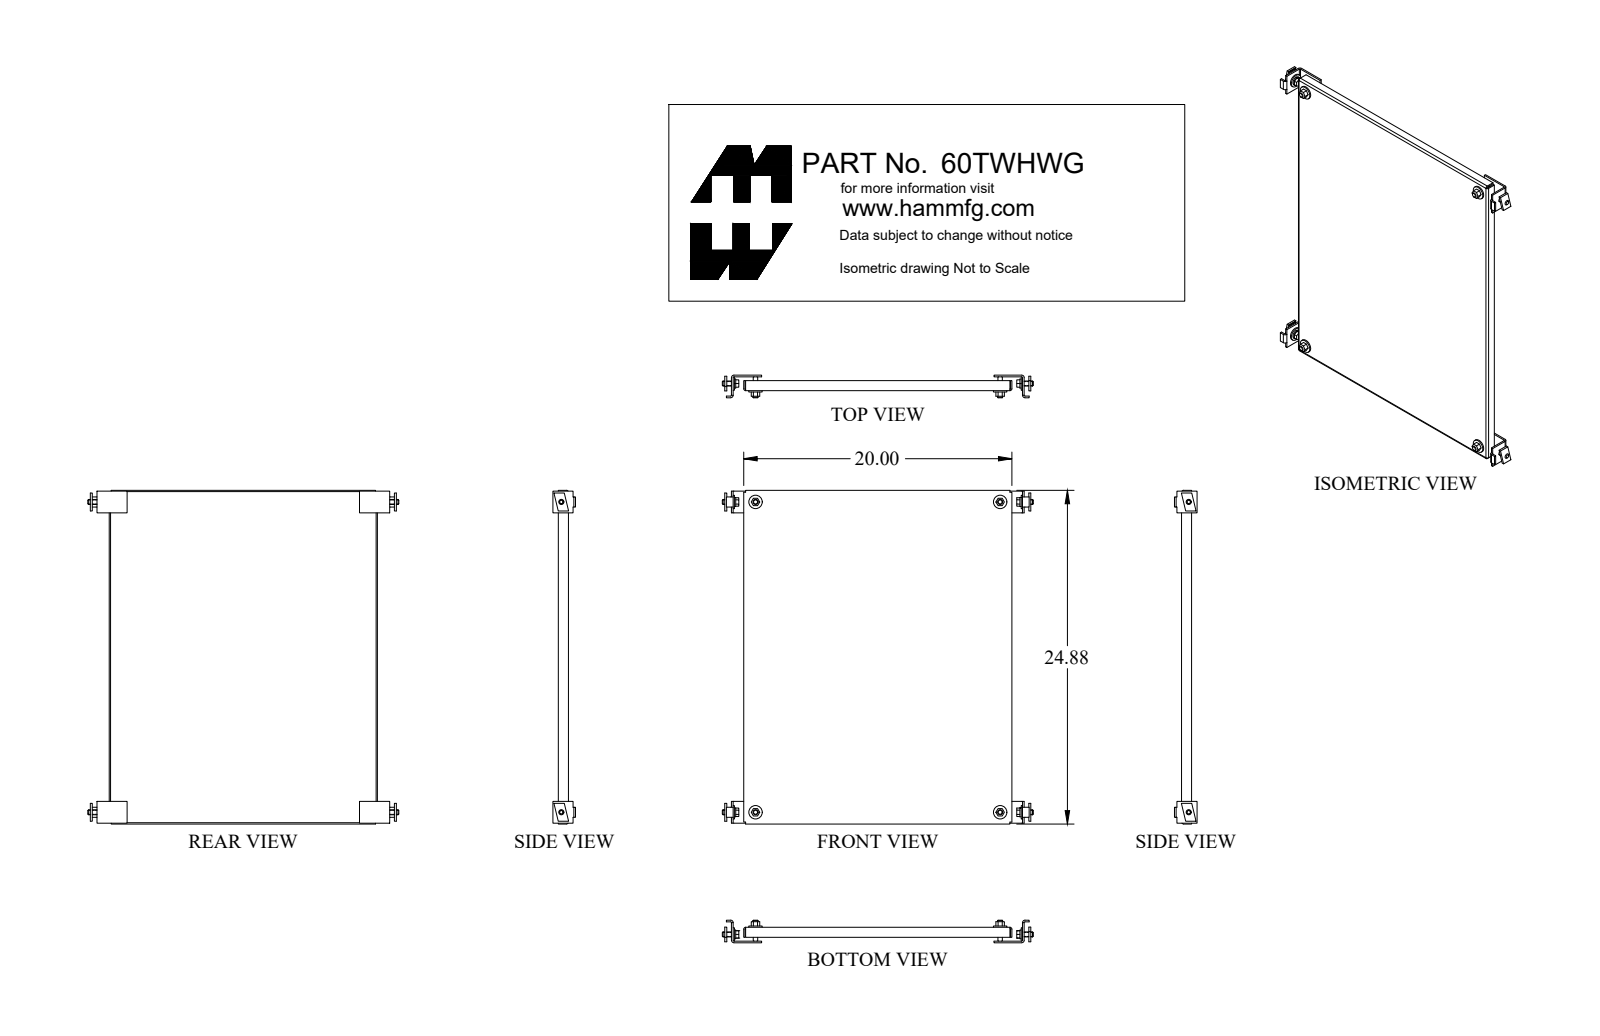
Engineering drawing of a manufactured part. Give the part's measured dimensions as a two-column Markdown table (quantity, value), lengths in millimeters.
| quantity | value |
| --- | --- |
| part name | 60TWHWG_Default |
| STEP written by | SolidWorks 2018 (CONFIG_CONTROL_DESIGN) |
| units | millimeters |
| bodies | 9 solids, 190 faces (94 planar, 64 cylindrical, 32 other) |
| overall size | 631.8 × 573.6 × 42.8 |
| volume | 918 200 mm³ |
| surface area | 758 100 mm² |
| round holes (diameter × count) | 14.3 × 4, 11.1 × 2 |
| round bosses / shafts (diameter × count) | 16.5 × 4, 9.5 × 4, 8.4 × 4 |
| partial cylindrical surfaces (radius × count) | 1.2 × 4, 1.5 × 4, 3.6 × 4, 4.7 × 4 |
| main face-to-face distances | 2.4, 505.6, 629.4, 3.2, 503.2, 508, 26.2, 23.8, 29.4, 27 |
| hole center spacings | 463.6, 587.4, 748.3, 587.5 |
